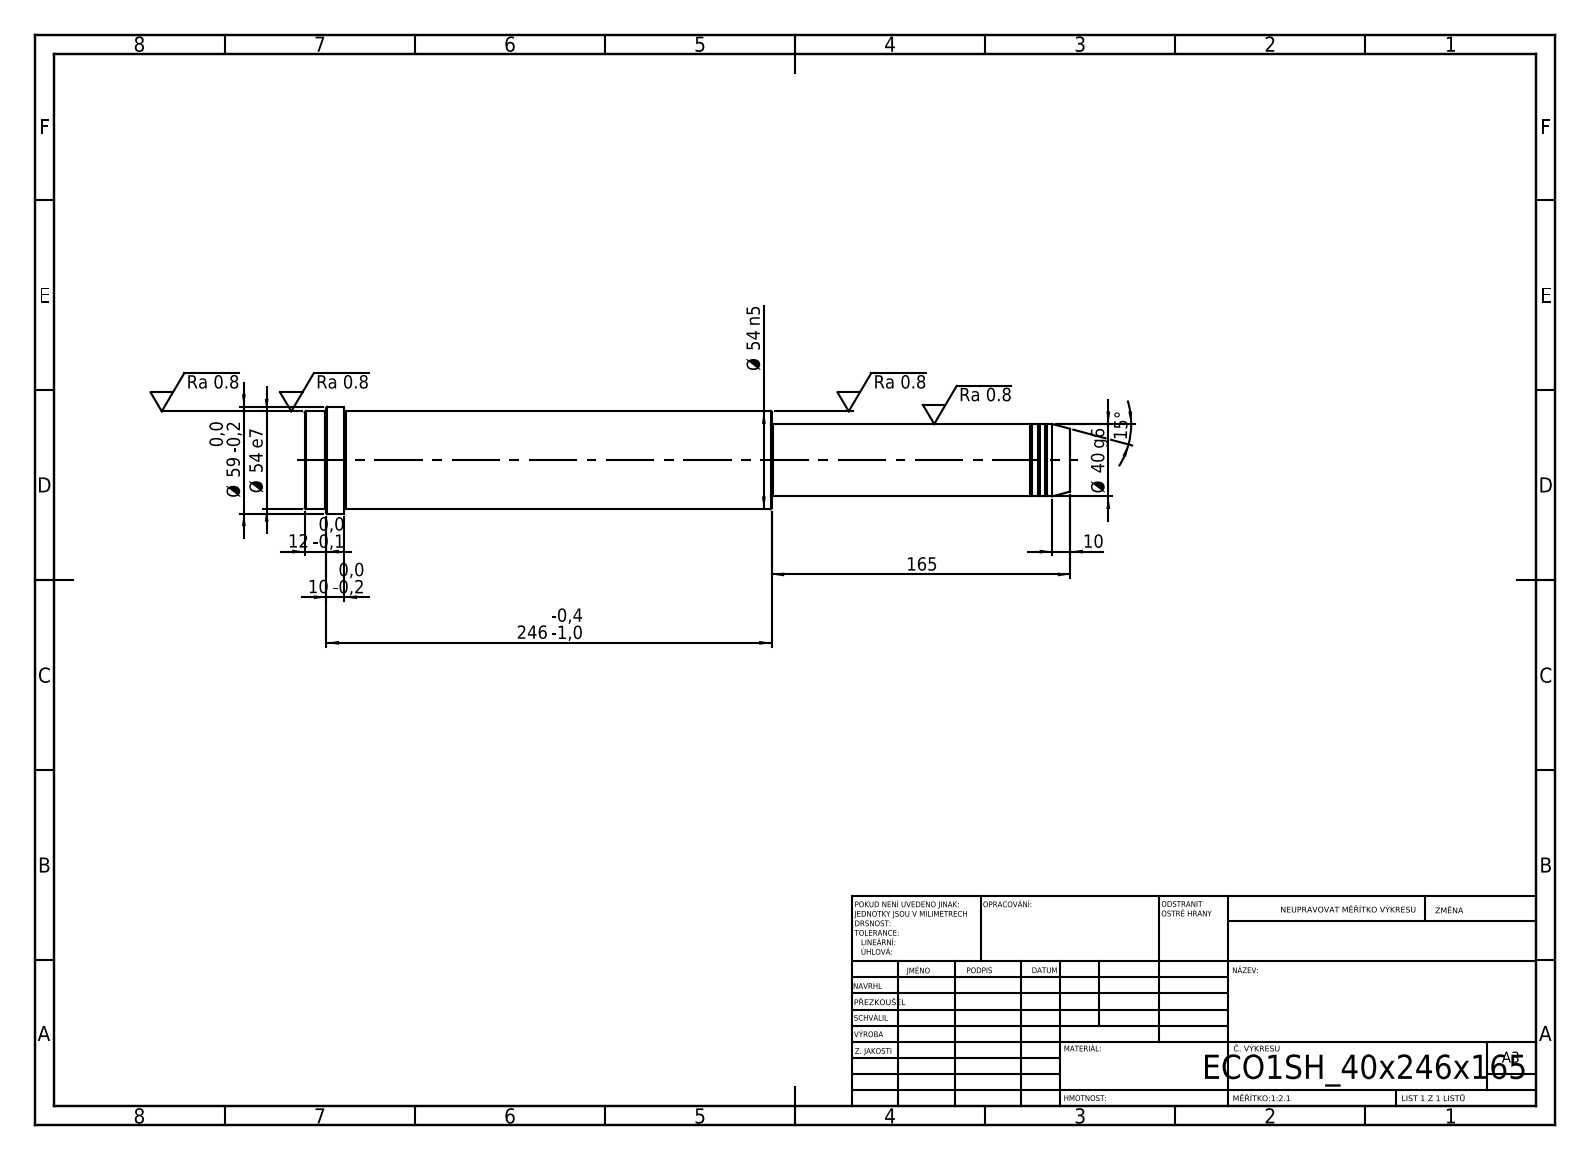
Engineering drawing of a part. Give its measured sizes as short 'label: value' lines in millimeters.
written by: SolidWorks 2019 (CONFIG_CONTROL_DESIGN)
unit: mm
bodies: 1 solid, 52 faces (6 planar, 16 cylindrical, 30 other)
size: 423 × 59 × 59
volume: 800 642 mm³; area: 70 118 mm²
bosses: 1× ⌀59, 1× ⌀54, 1× ⌀40, 1× ⌀39
face distances: 258, 165, 423, 401, 236, 22, 411, 246, 10, 12
